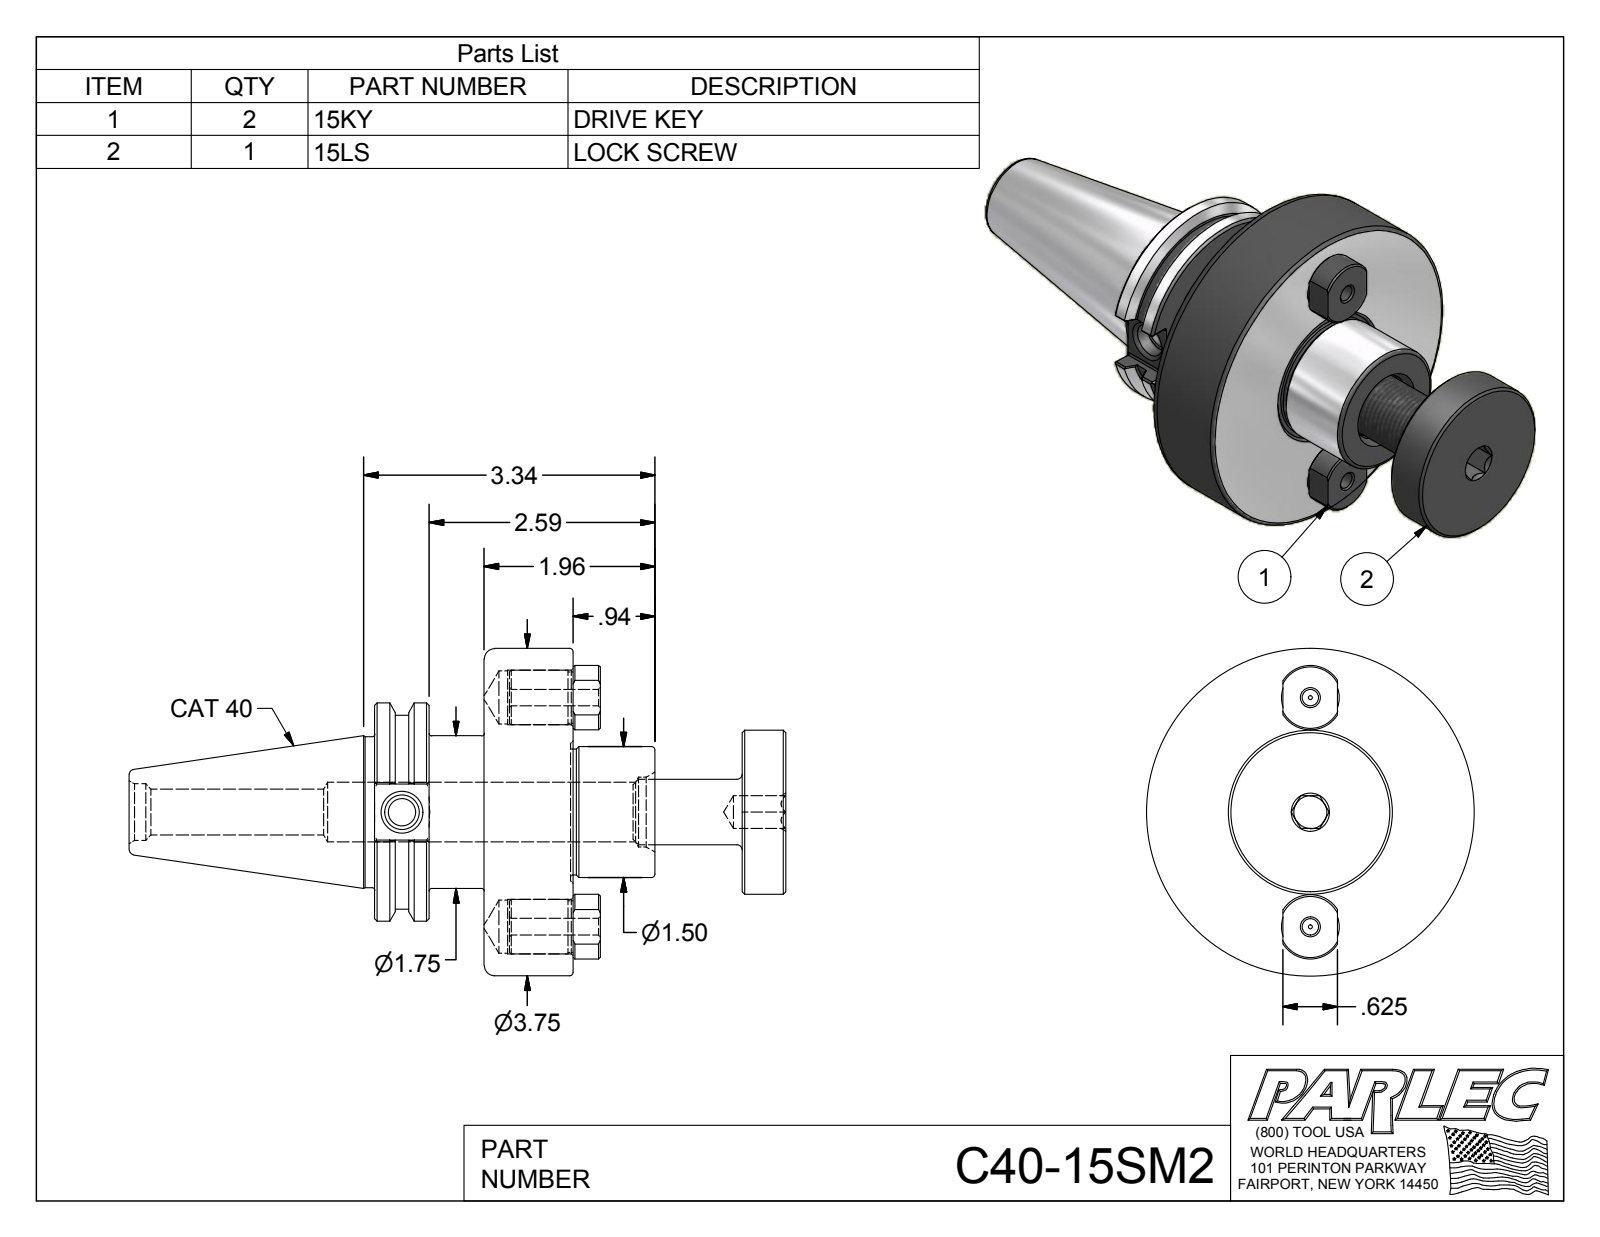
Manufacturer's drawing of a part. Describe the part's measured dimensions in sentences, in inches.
The part is named "C40-15SM2; C40-15SM2-1; 15LS; 15KY". Its 3-D file was written by "Autodesk Inventor 2012 (AUTOMOTIVE_DESIGN)". It is 4 solids with 168 faces: 63 planar, 46 cylindrical and 59 other. Overall it measures 7.524 by 3.75 by 3.75 inches. Its volume is 21.28 cubic inches and its surface area 95.95 square inches. Round holes: 2 of diameter 0.19, 2 of diameter 0.609, 2 of diameter 0.624, 1 of diameter 0.315, 1 of diameter 0.375, 1 of diameter 0.399, 1 of diameter 0.527, 1 of diameter 0.648, 1 of diameter 0.682, 1 of diameter 0.8. Round bosses or shafts: 2 of diameter 0.626, 2 of diameter 0.59, 1 of diameter 3.75, 1 of diameter 2.5, 1 of diameter 2.219, 1 of diameter 1.88, 1 of diameter 1.75, 1 of diameter 1.73. Partial cylindrical surfaces (rounded edges, fillets, slot ends): 12 of radius 0.02, 2 of radius 0.37. The main face-to-face distances are 1.02, 3.457, 2.437, 2.957, 1.937, 0.5, 1.255, 2.275, 4.212, 4.712. The hole center spacings are 1.312, 1.312, 2.624.
